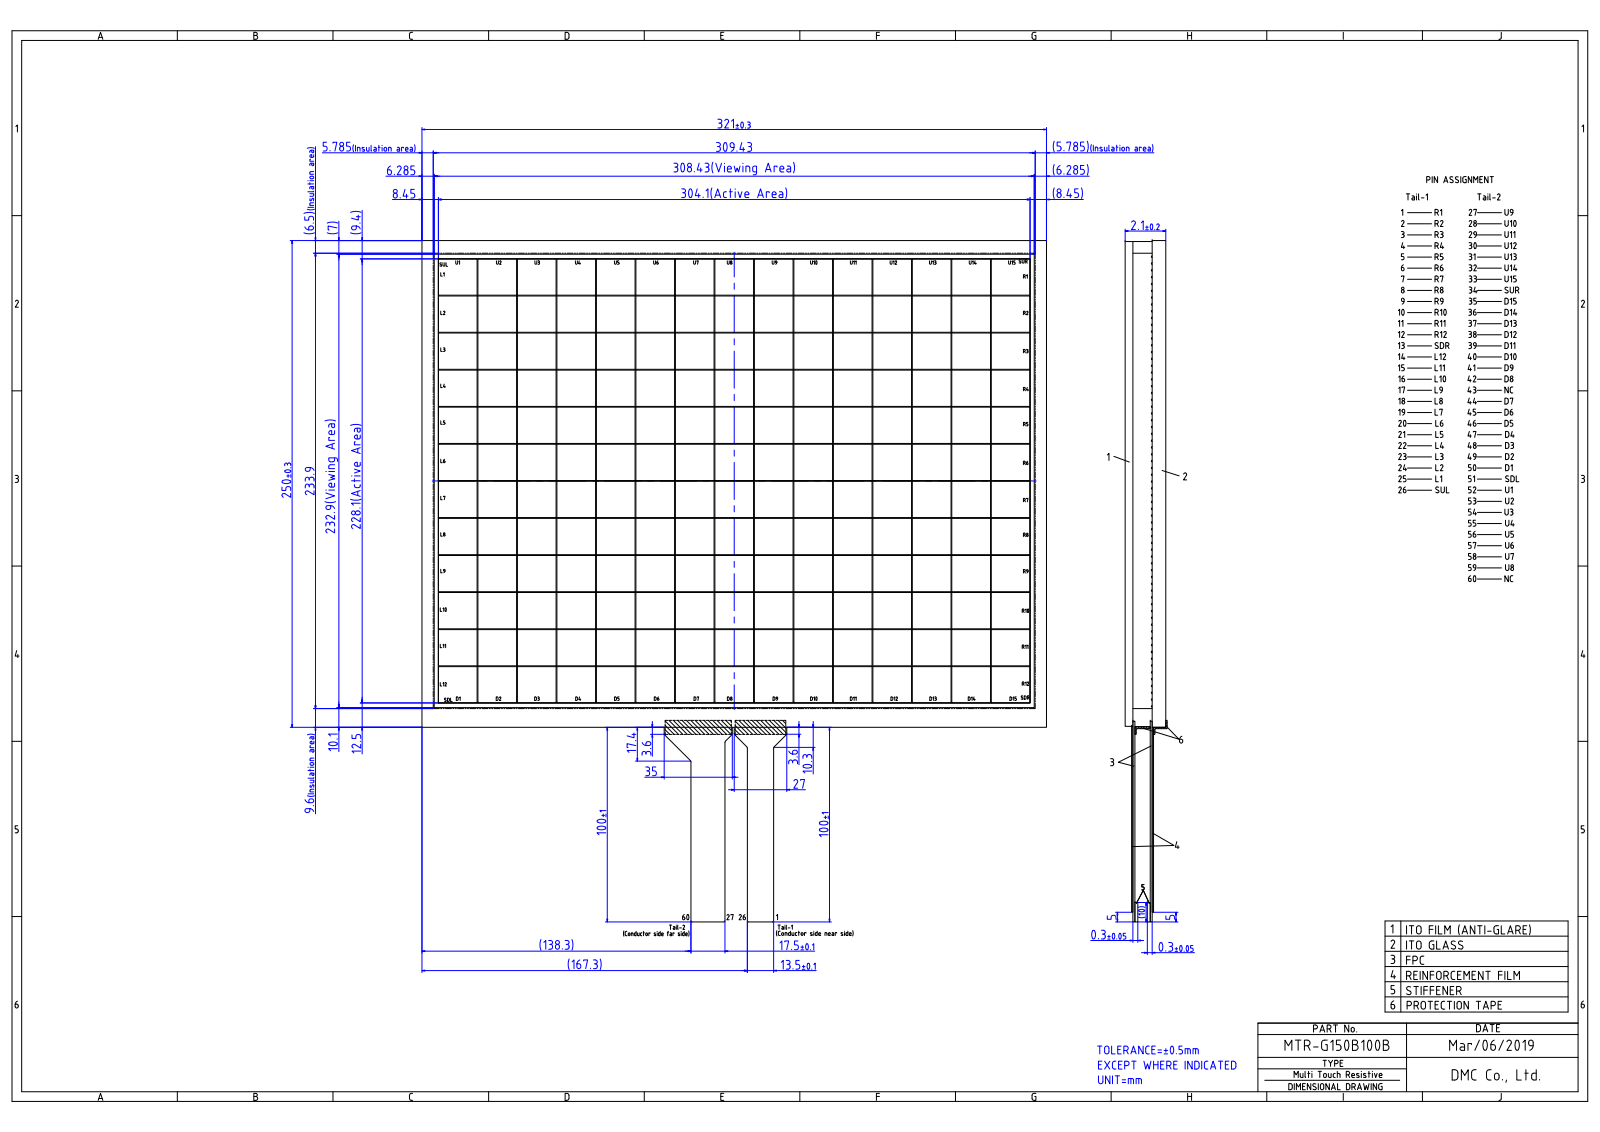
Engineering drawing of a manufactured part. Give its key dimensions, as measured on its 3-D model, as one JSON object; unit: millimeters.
{"part_name": "MTR-G150B100B", "step_written_by": "Autodesk Inventor 2020 (CONFIG_CONTROL_DESIGN)", "units": "millimeters", "bodies": {"solids": 1, "faces": 294, "planar": 282, "cylindrical": 12, "other": 0}, "overall_size": [449.4, 400, 2.2], "volume_mm3": 168691, "surface_area_mm2": 169903, "partial_cylinders_radius": [[1, 8], [0.2, 4]], "face_to_face_distances": [2.1, 1.8, 1.9, 2, 250, 321, 0.4, 2.2, 0.5, 0.7]}
